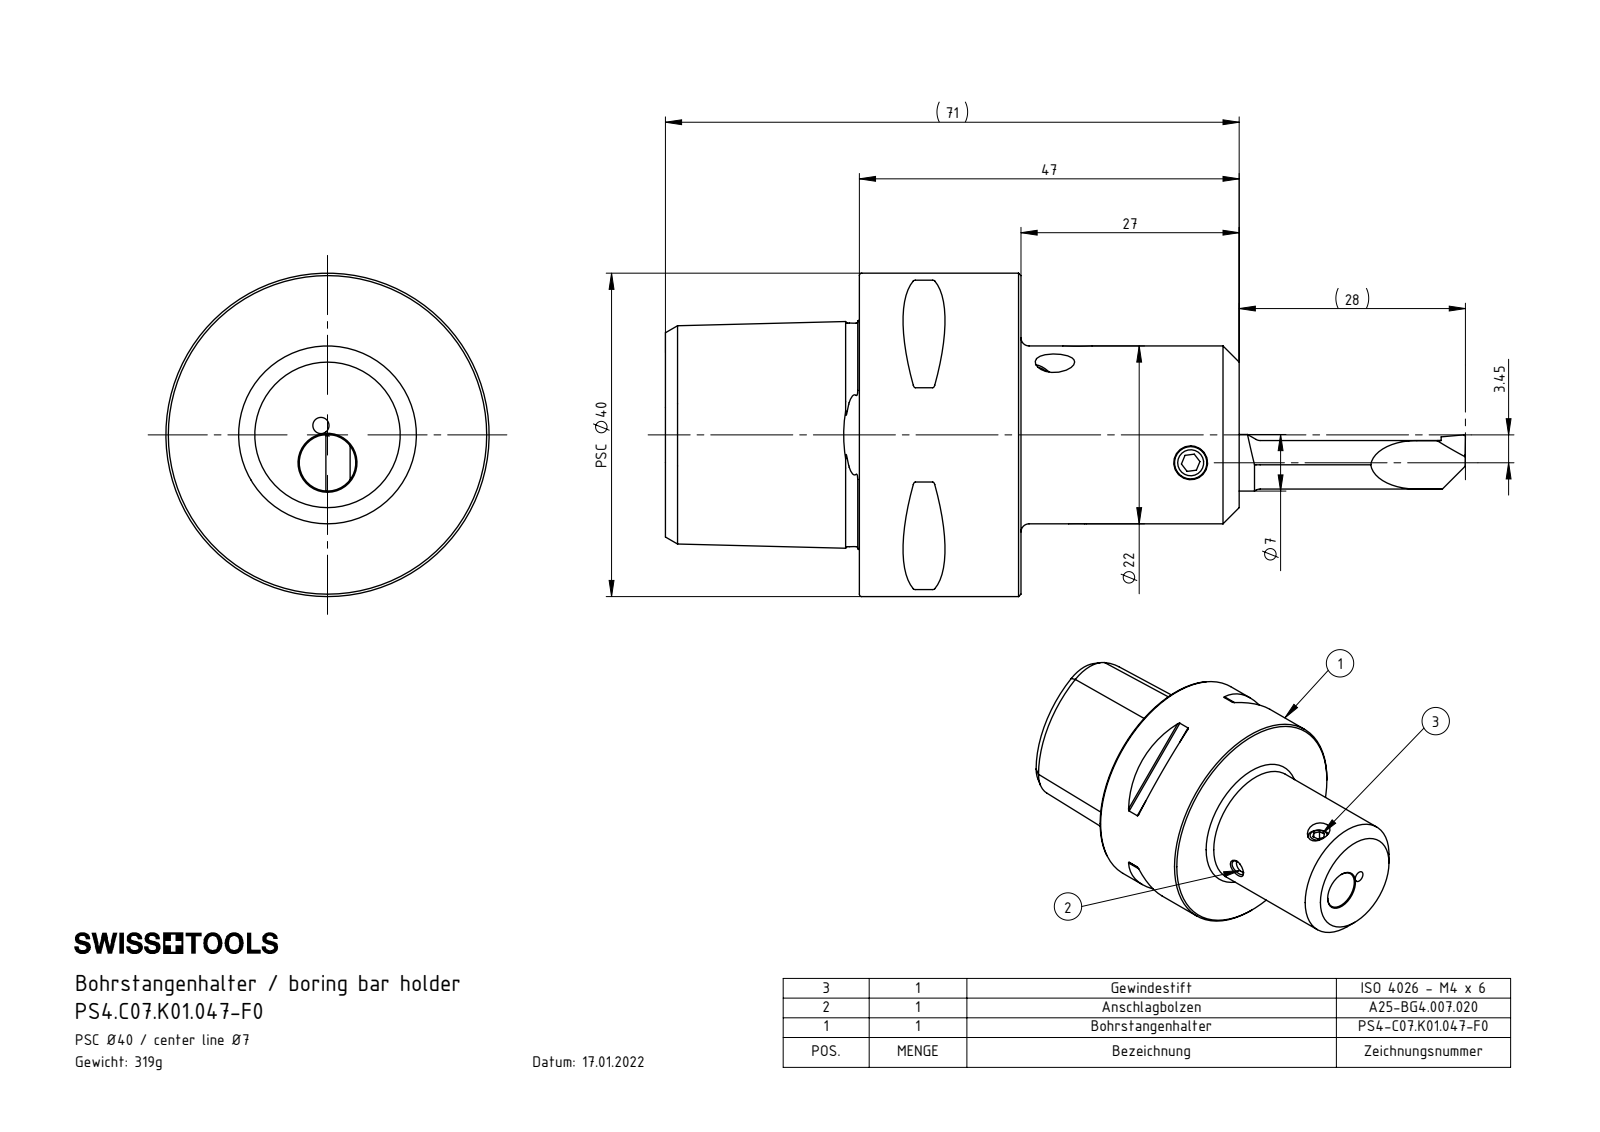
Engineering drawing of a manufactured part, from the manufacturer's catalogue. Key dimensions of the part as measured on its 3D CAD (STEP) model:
Part name (STEP PRODUCT): KVT_MB_600_040; Axx-BG4.003.xxx_A_Adapter 7; PS4.C07.K01.047-F0; PS4-C07.K01.047-F0_A (+1 more)
STEP written by: SolidWorks 2017 (AUTOMOTIVE_DESIGN)
Units: millimetres
Bodies: 5 solids, 165 faces (45 planar, 36 cylindrical, 84 other)
Overall size (bounding box): 71 × 40 × 40
Volume: 40 607 mm³ · Surface area: 12 184 mm²
Round holes (diameter × count): ⌀3.3 ×3, ⌀2 ×2, ⌀3 ×2, ⌀4 ×2, ⌀4.2 ×1, ⌀4.5 ×1, ⌀4.6 ×1, ⌀5 ×1, ⌀7 ×1, ⌀12.5 ×1, ⌀18 ×1, ⌀20 ×1
Round bosses / shafts (diameter × count): ⌀4 ×3, ⌀40 ×1, ⌀22 ×1, ⌀2.7 ×1
Partial cylindrical surfaces — rounded edges, fillets, slot ends (radius × count): R0.3 ×8, R3 ×1
Main face-to-face distances: 20, 47, 27, 24, 44, 71, 15.52, 35.3, 15, 9
Hole centre spacings: 3.45, 23.5, 29.2, 52.61
